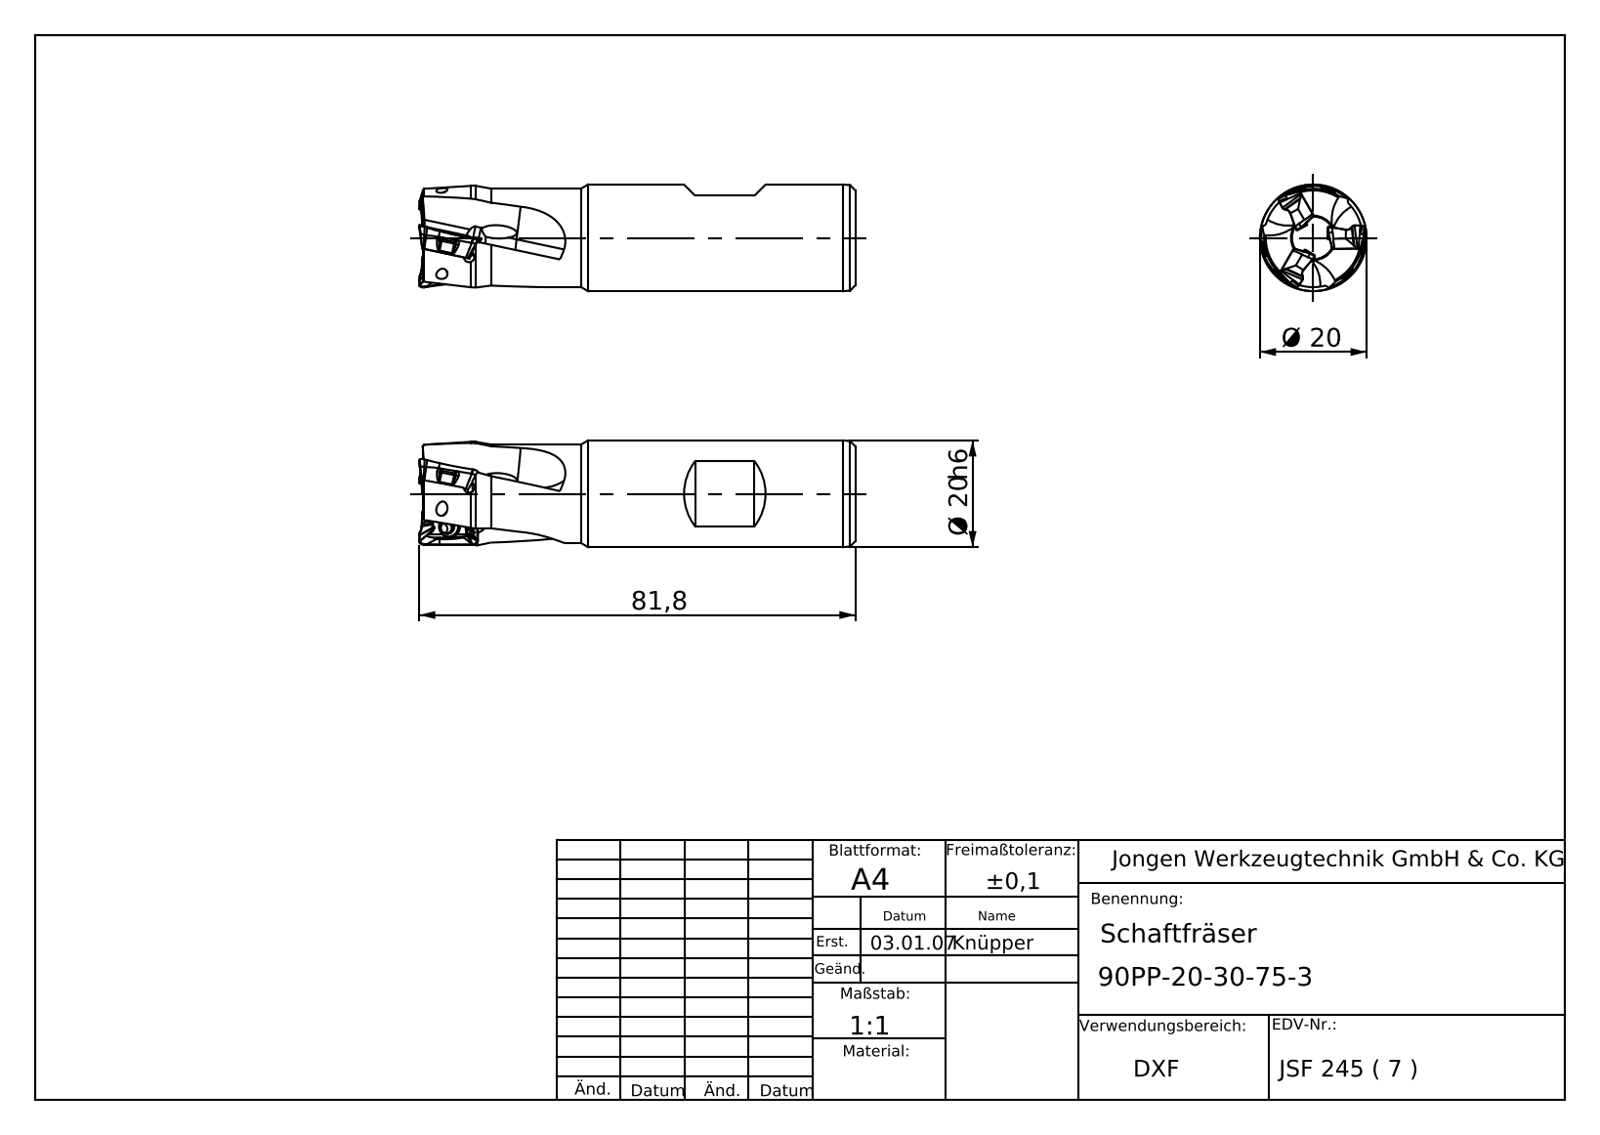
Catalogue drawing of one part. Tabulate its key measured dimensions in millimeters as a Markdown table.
| quantity | value |
| --- | --- |
| part name | 90PP-20-30-75-3 |
| STEP written by | SolidWorks 2012 (AUTOMOTIVE_DESIGN) |
| units | millimeters |
| bodies | 1 solid, 74 faces (23 planar, 22 cylindrical, 29 other) |
| overall size | 81.8 × 20.35 × 20 |
| volume | 22 124 mm³ |
| surface area | 7 036 mm² |
| round holes (diameter × count) | 2.5 × 3, 4 × 1 |
| round bosses / shafts (diameter × count) | 20 × 1, 18.5 × 1 |
| partial cylindrical surfaces (radius × count) | 1.47 × 9 |
| main face-to-face distances | 80.42 |
